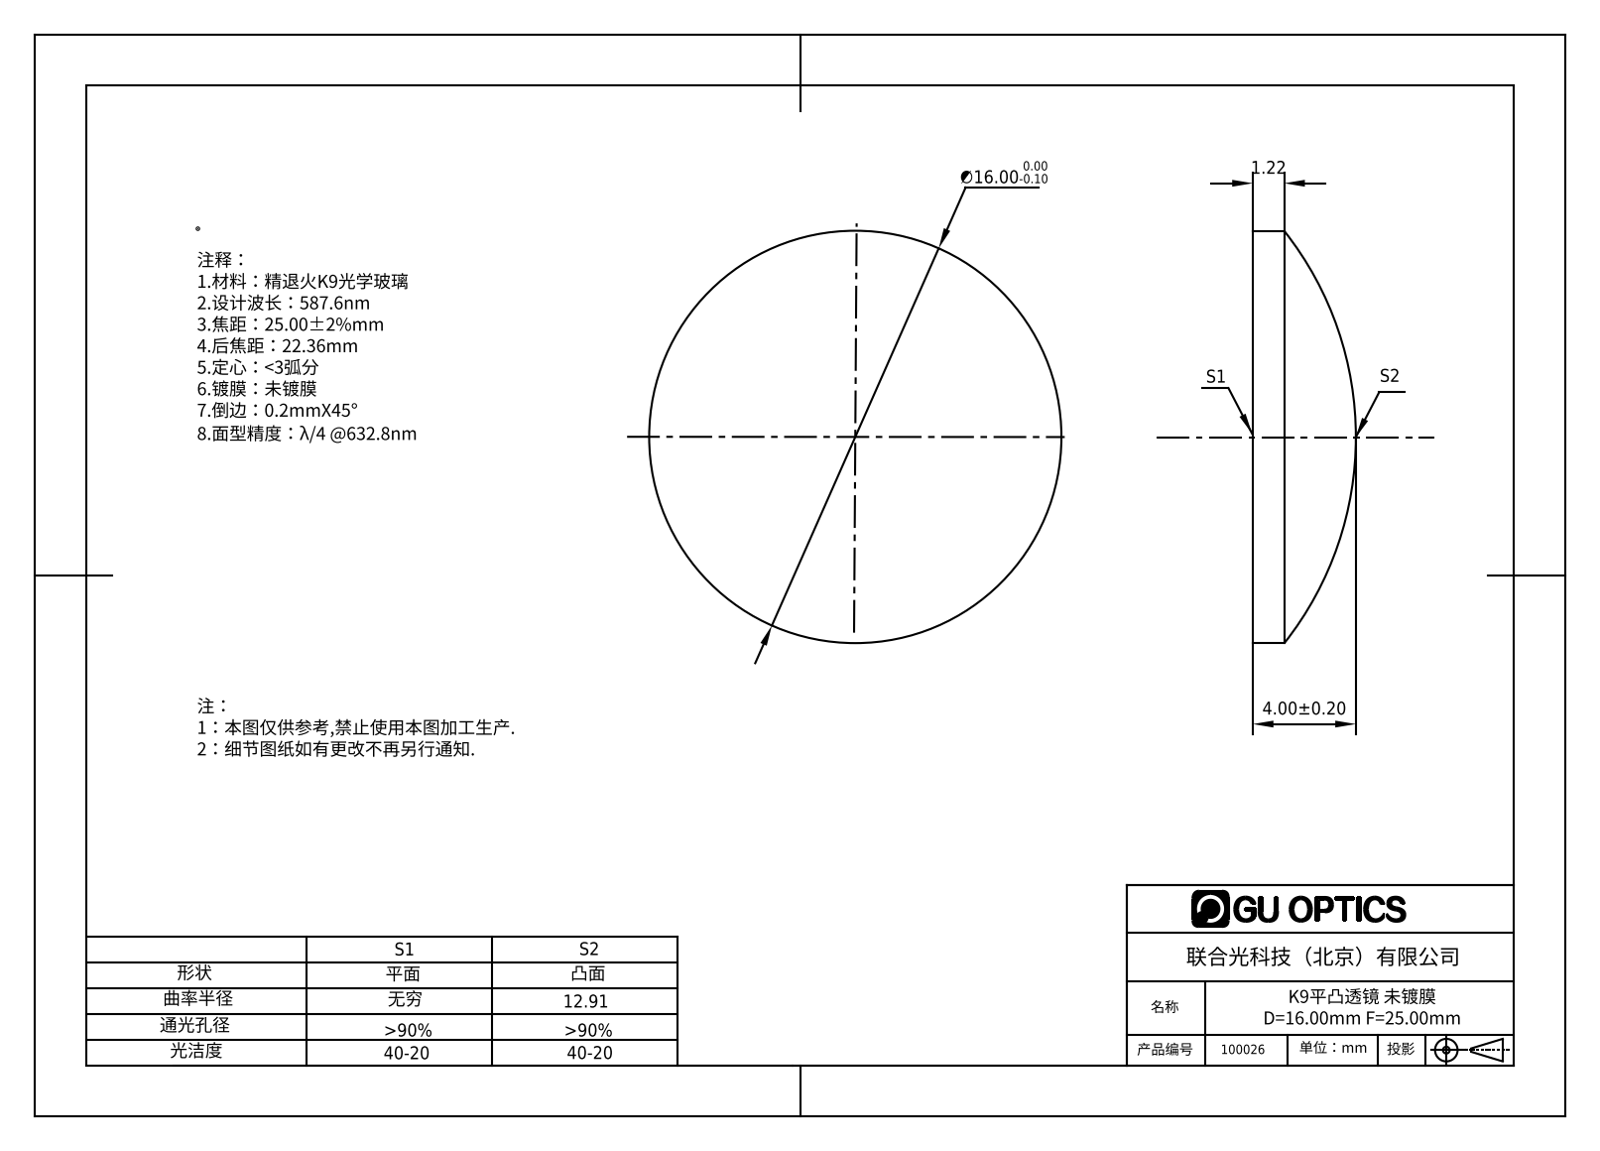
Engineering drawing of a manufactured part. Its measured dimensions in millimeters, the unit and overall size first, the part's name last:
Units: millimetres
Overall size (bounding box): 16 × 16 × 4
Round bosses / shafts (diameter × count): ⌀16 ×1
Volume: 536 mm³ · Surface area: 488 mm²
Bodies: 1 solid, 5 faces (1 planar, 2 cylindrical, 2 other)
Part name (STEP PRODUCT): 100026
STEP written by: SolidWorks 2016 (AUTOMOTIVE_DESIGN)
